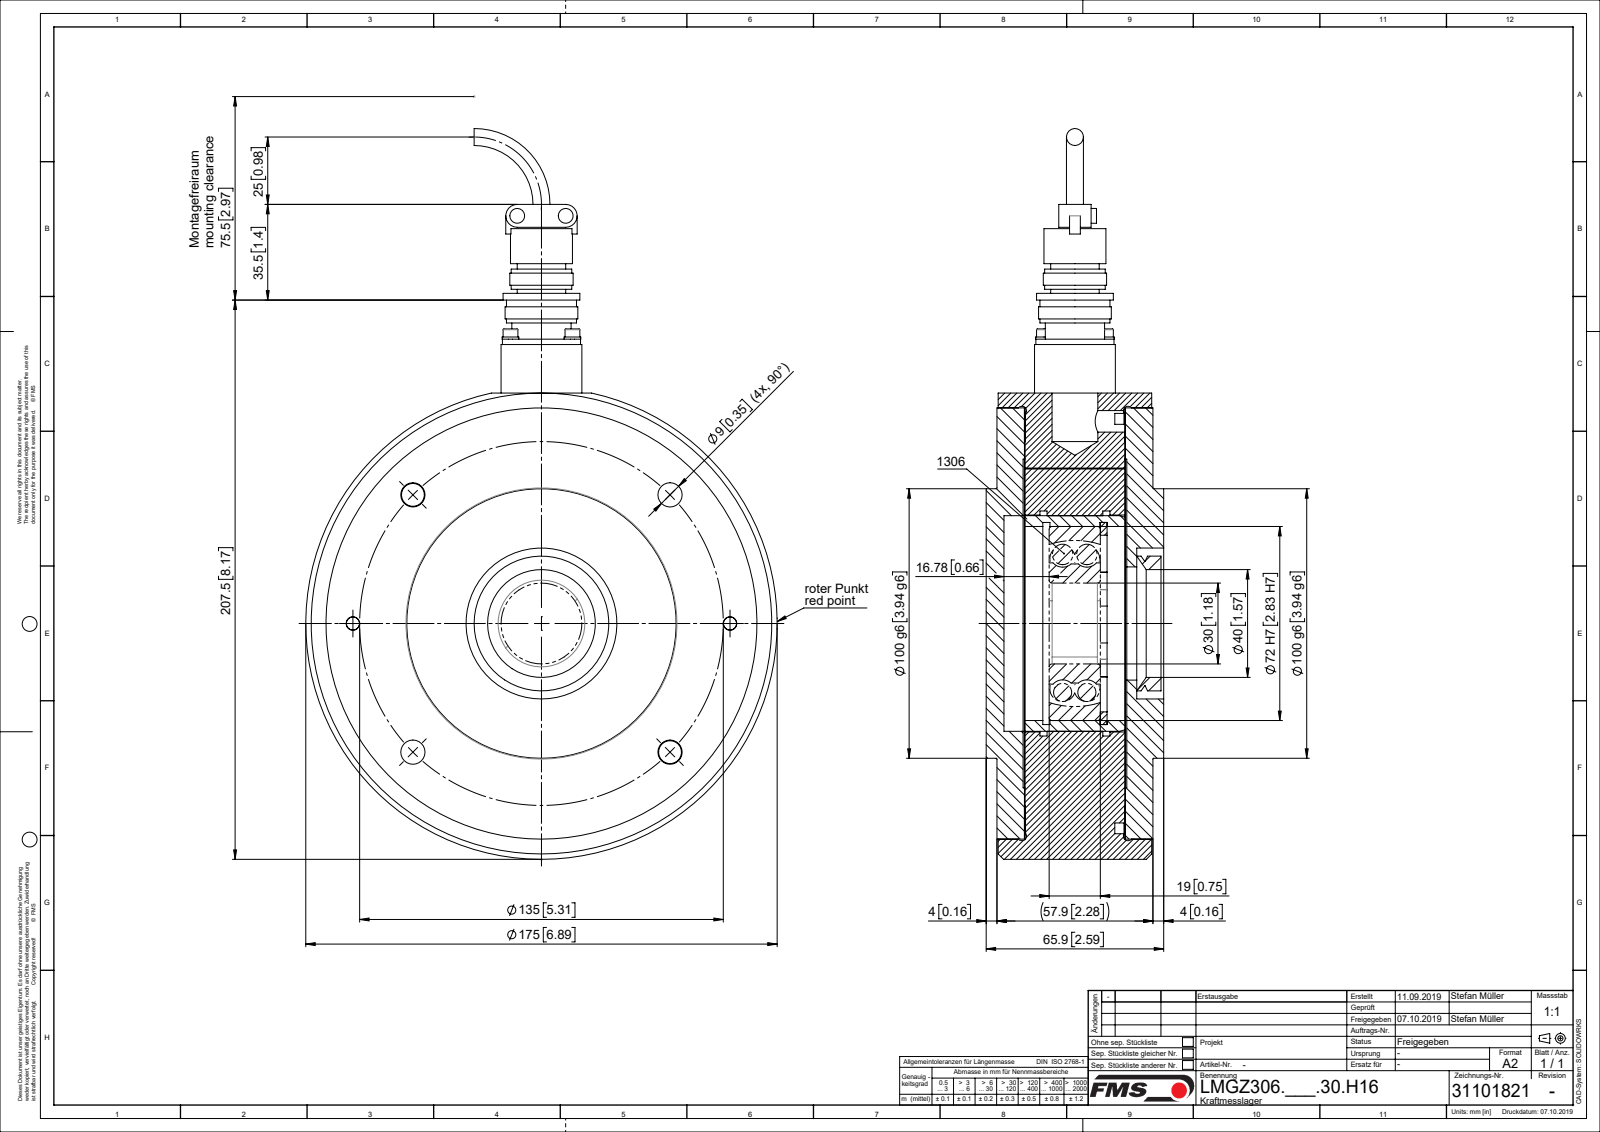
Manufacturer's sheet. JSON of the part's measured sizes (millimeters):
{"part_name": "L50324_STP; L4974404; TEIL1; L49745 (+8 more)", "step_written_by": "Mechanical Desktop 2009 (CONFIG_CONTROL_DESIGN)", "units": "millimeters", "bodies": {"solids": 22, "faces": 409, "planar": 106, "cylindrical": 241, "other": 62}, "overall_size": [271.15, 175, 65.9], "volume_mm3": 1286000, "surface_area_mm2": 271541, "round_holes": [[2.6, 4], [3.2, 4], [3.4, 4], [9, 4], [5, 2], [6.6, 2], [8, 2], [8.68, 2], [11, 2], [10, 1], [17, 1], [23, 1]], "round_bosses_or_shafts": [[5.5, 6], [6.2, 4], [3, 4], [2.5, 4], [10, 2], [6, 2], [175, 1], [160, 1]], "partial_cylinders_radius": [[4.25, 2], [7.5, 2]], "face_to_face_distances": [37.25, 10.2, 10.45, 47.45, 47.7, 38, 37, 0.5, 9.7, 48.2], "hole_center_spacings": [16.26, 23, 48.72, 52.67, 67.5, 95.46, 115.55, 127.04]}
